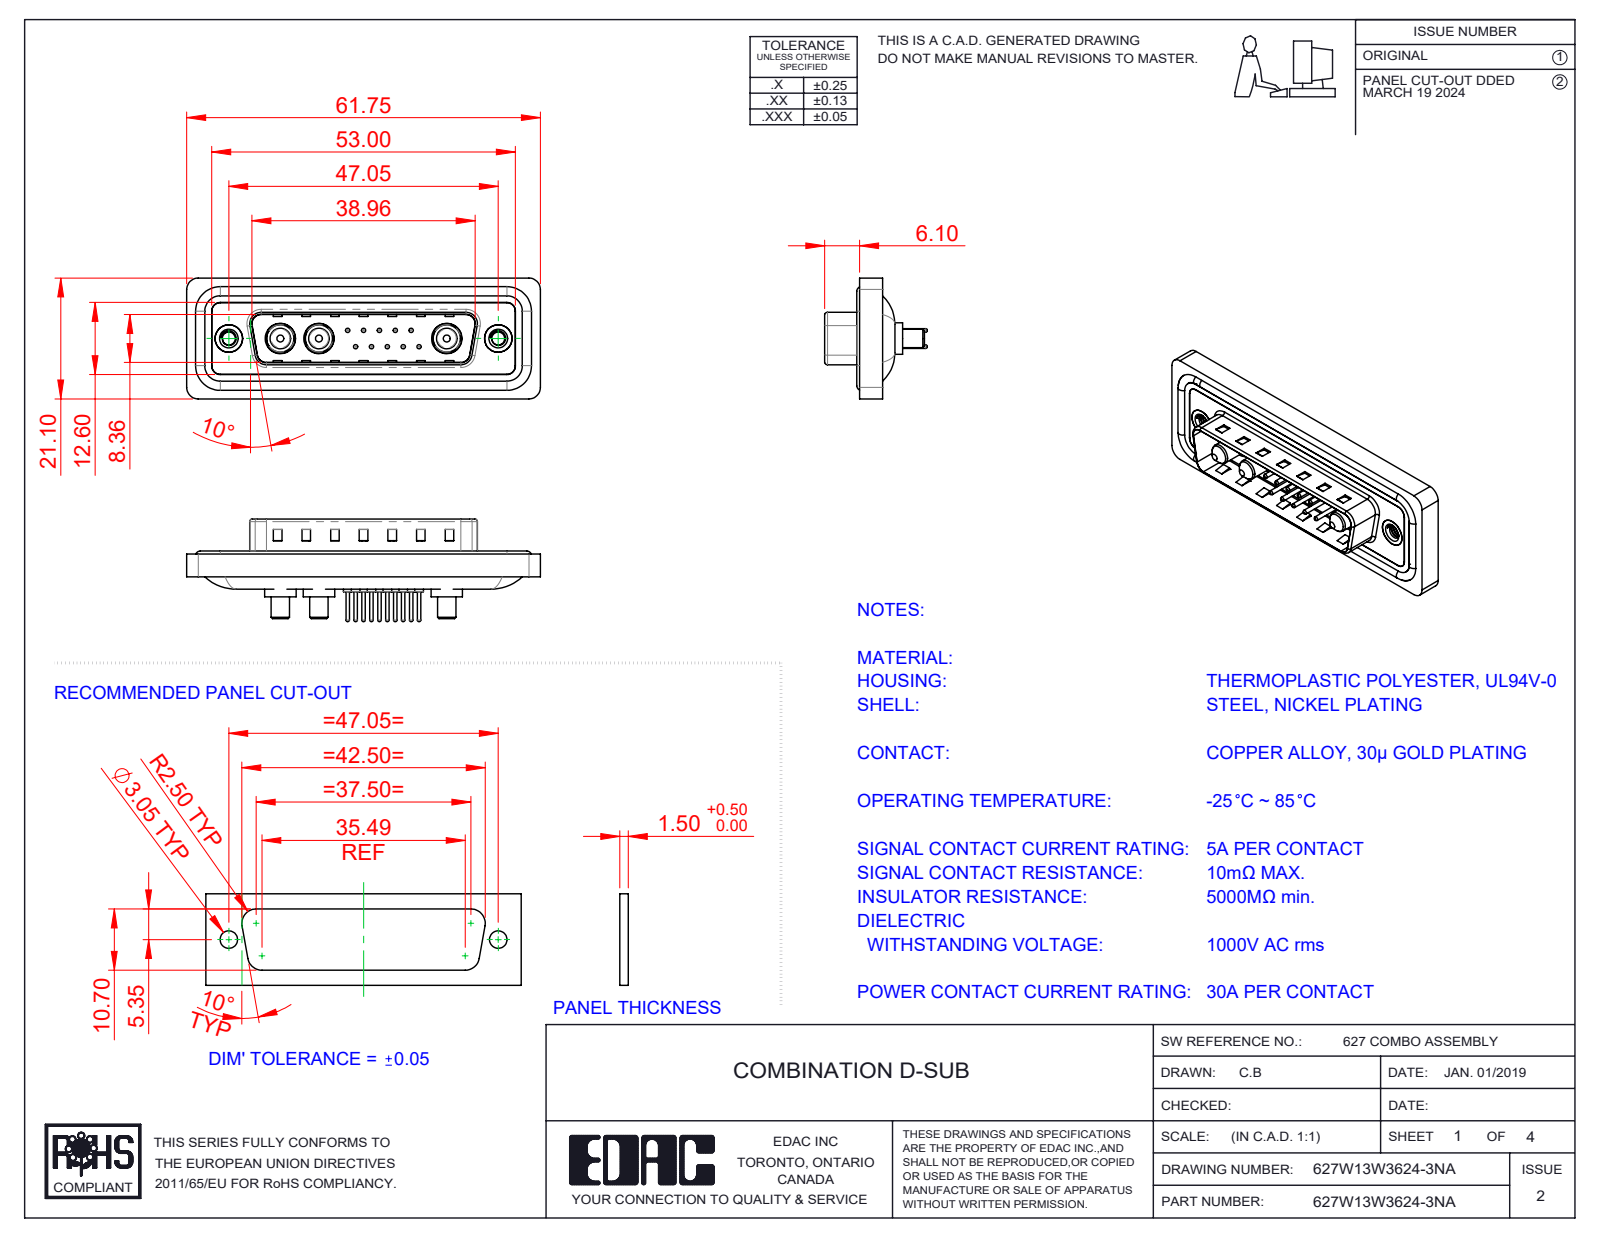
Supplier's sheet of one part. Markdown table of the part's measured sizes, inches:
| quantity | value |
| --- | --- |
| part name | 627Combo Shell Rear_25 Contacts; 627Combo Contact Row 1_24; 627Combo Contact Row 2_24; 627Combo Housing_13W3 (+5 more) |
| STEP written by | SolidWorks 2023 (CONFIG_CONTROL_DESIGN) |
| units | inches |
| bodies | 23 solids, 968 faces (309 planar, 387 cylindrical, 272 other) |
| overall size | 2.431 × 0.831 × 0.705 |
| volume | 0.449 in³ |
| surface area | 18.42 in² |
| round holes (diameter × count) | 0.03 × 10, 0.063 × 10, 0.079 × 10, 0.191 × 3, 0.209 × 3, 0.089 × 2, 0.157 × 2, 0.189 × 2, 0.197 × 2 |
| round bosses / shafts (diameter × count) | 0.059 × 10, 0.024 × 10, 0.063 × 4, 0.217 × 3, 0.205 × 3, 0.187 × 3, 0.148 × 3, 0.142 × 3 |
| partial cylindrical surfaces (radius × count) | 0.059 × 22, 0.079 × 18, 0.02 × 8, 0.063 × 8, 0.01 × 4, 0.024 × 4, 0.026 × 4, 0.035 × 4 |
| main face-to-face distances | 0.016, 0.059, 0.043, 0.063, 0.02, 0.122, 0.114, 0.032, 0.377, 0.161 |
| hole center spacings | 0.124, 0.109, 0.198, 0.218, 0.295, 0.198, 0.327, 0.398 |
